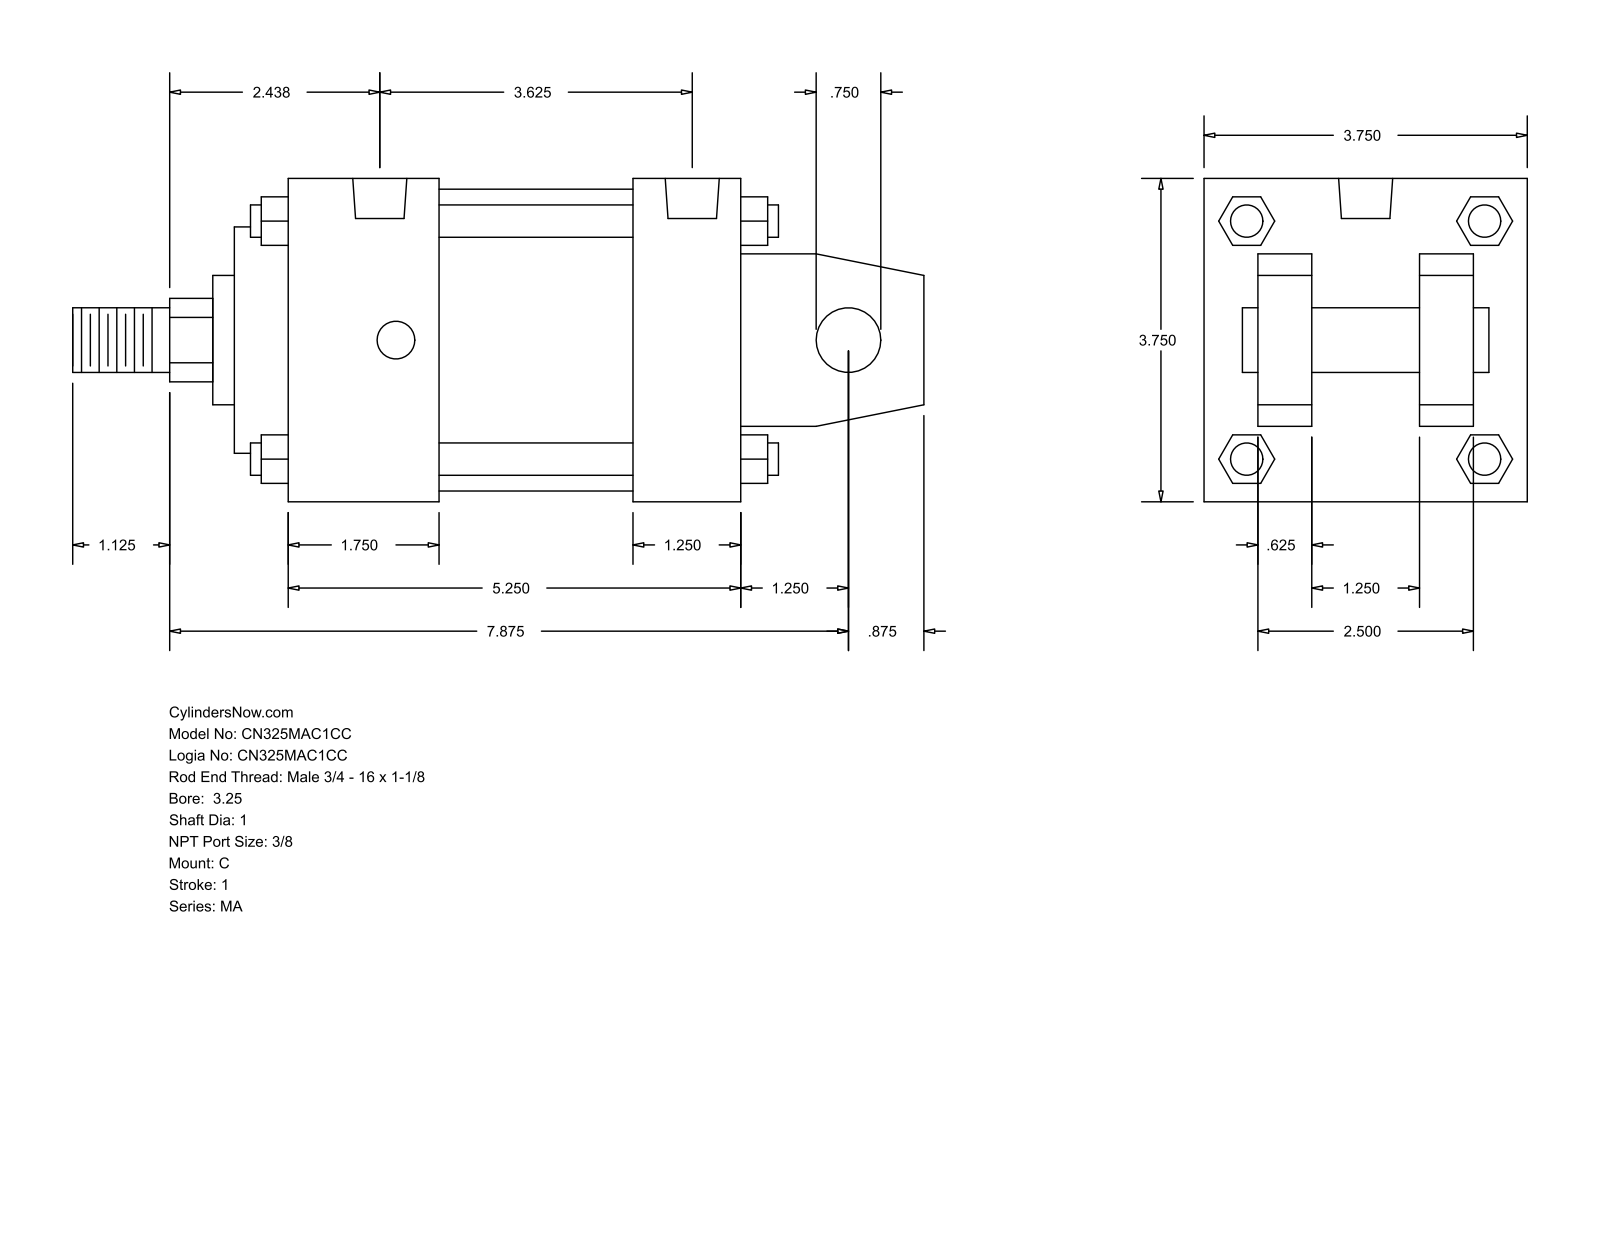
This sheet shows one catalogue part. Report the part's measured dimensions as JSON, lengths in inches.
{"part_name": "MA_C__0325_1", "step_written_by": "GSSL Pune (CONFIG_CONTROL_DESIGN)", "units": "inches", "bodies": {"solids": 0, "faces": 141, "planar": 109, "cylindrical": 32, "other": 0}, "overall_size": [9.875, 3.75, 3.75], "round_holes": [[0.437, 4], [0.627, 2]], "round_bosses_or_shafts": [[0.375, 4], [0.75, 2], [3.5, 1], [2.625, 1], [1.5, 1], [1, 1]], "partial_cylinders_radius": [[0.484, 1]], "face_to_face_distances": [3.75, 0.625, 2.5, 5.25, 1.25, 3.125, 1.875, 4, 1.25, 1.75], "hole_center_spacings": [3.25, 0.187, 0.188, 3.437, 3.438, 3.625]}
